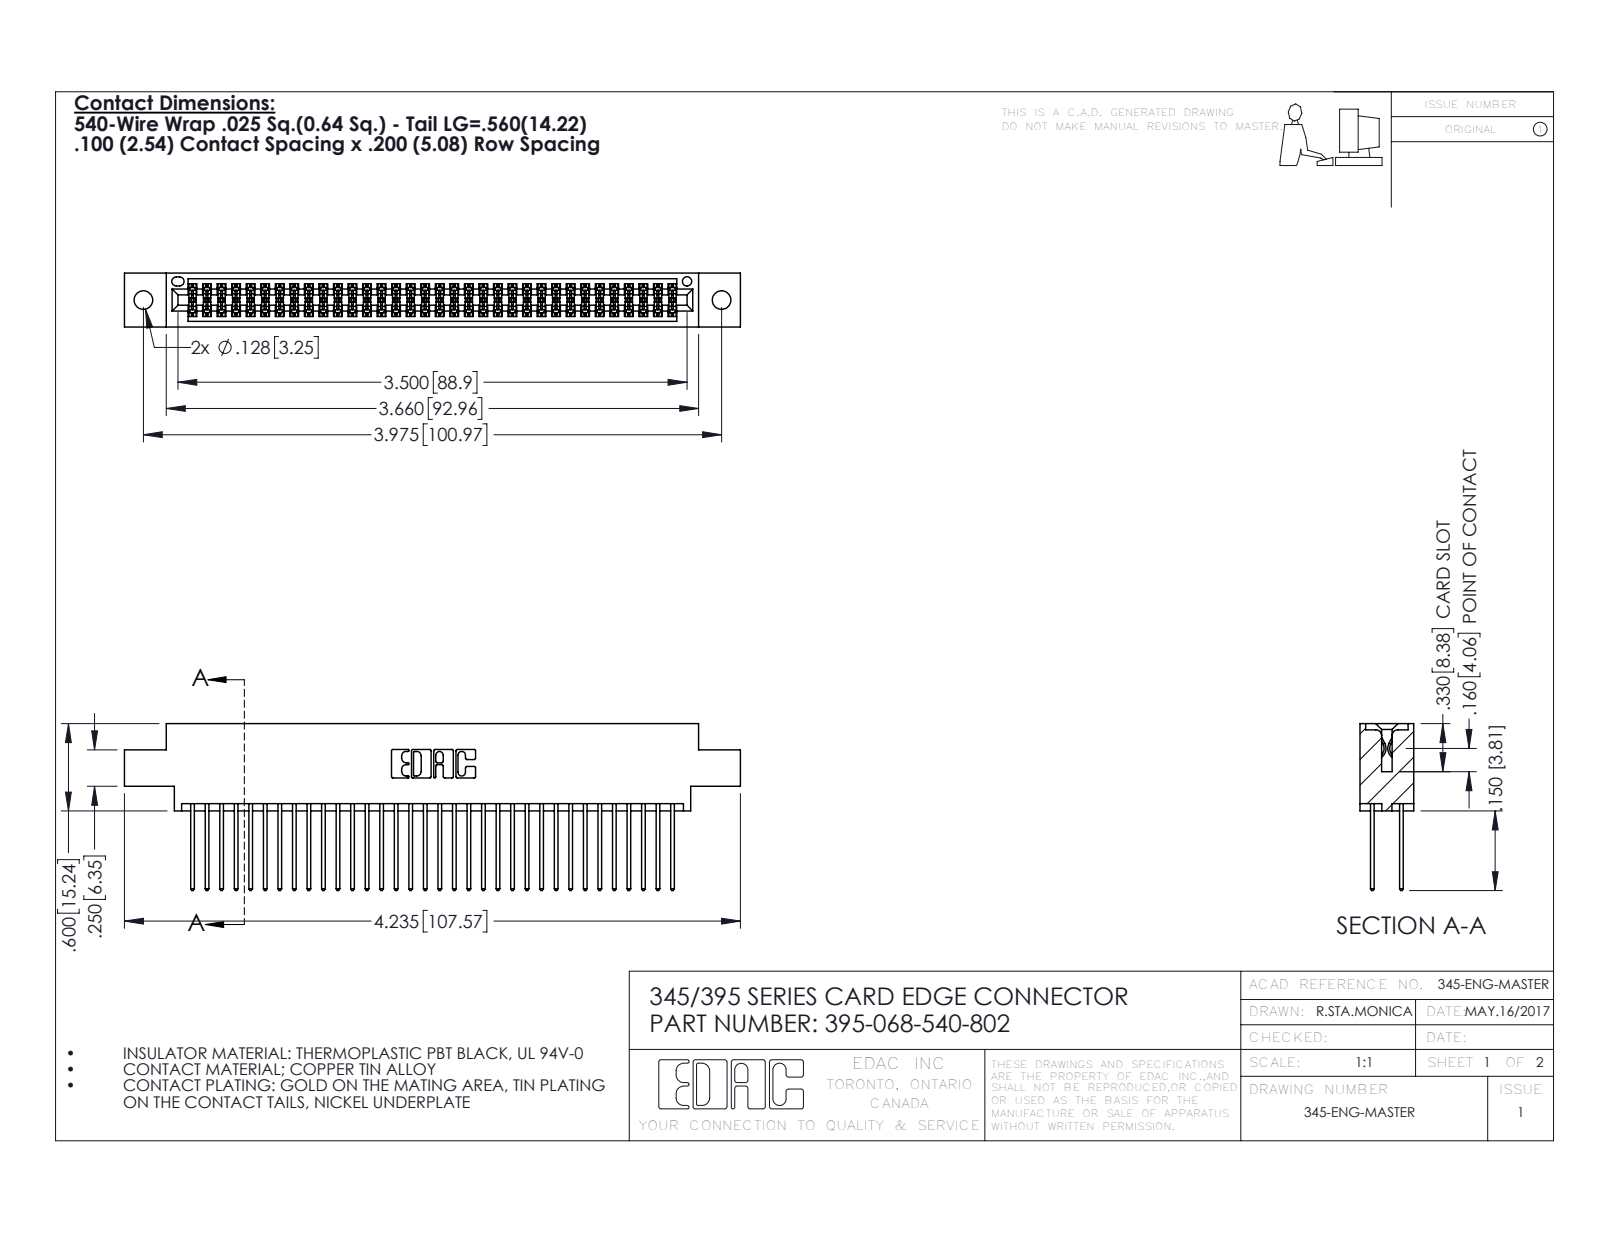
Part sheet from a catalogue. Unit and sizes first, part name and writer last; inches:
Units: inches
Overall size (bounding box): 4.235 × 1.147 × 0.37
Round holes (diameter × count): ⌀0.128 ×2, ⌀0.064 ×1
Partial cylindrical surfaces — rounded edges, fillets, slot ends (radius × count): R0.006 ×102, R0.01 ×68, R0.01 ×22, R0.007 ×6, R0.031 ×6, R0.026 ×3, R0.014 ×2, R0.019 ×2
Main face-to-face distances: 0.298, 0.072, 0.2, 0.098, 0.272, 0.025, 0.37, 0.225, 0.175, 0.149
Hole centre spacings: 0.27, 3.74, 3.975
Volume: 0.64 in³ · Surface area: 25.43 in²
Bodies: 69 solids, 3530 faces (2328 planar, 1202 cylindrical, 0 other)
Part name (STEP PRODUCT): 395-068-540-802; 345-292-001_345-293-140; 345 Part_0.170 Offset - 0.128 Dia
STEP written by: SolidWorks 2016 (CONFIG_CONTROL_DESIGN)
